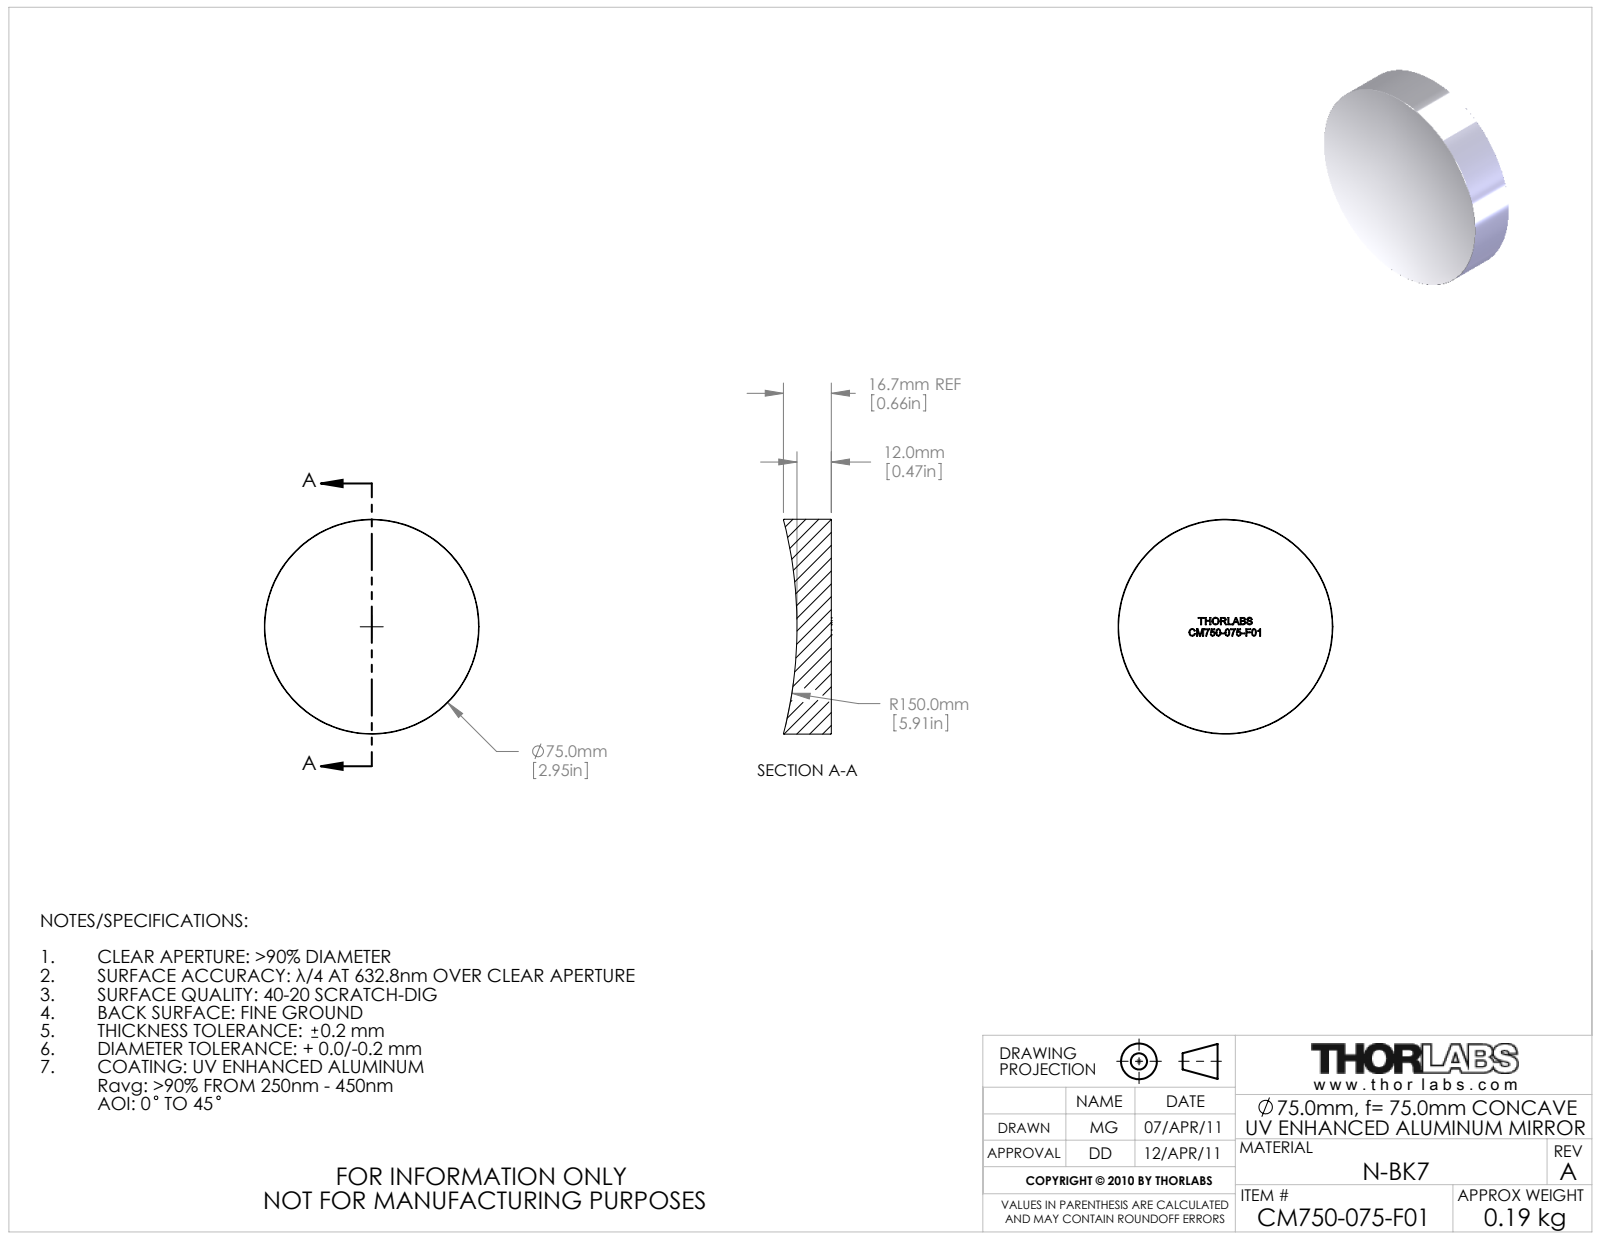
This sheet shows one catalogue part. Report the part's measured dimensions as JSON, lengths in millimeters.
{"part_name": "22202-E0W", "step_written_by": "SolidWorks 2011 (AUTOMOTIVE_DESIGN)", "units": "millimeters", "bodies": {"solids": 1, "faces": 267, "planar": 151, "cylindrical": 2, "other": 114}, "overall_size": [75, 75, 16.7], "volume_mm3": 63470, "surface_area_mm2": 12790, "round_bosses_or_shafts": [[75, 1]], "face_to_face_distances": [2.6, 0.4, 0.4, 6.3, 4, 4, 0.3, 1.4, 1.4, 1.6]}
